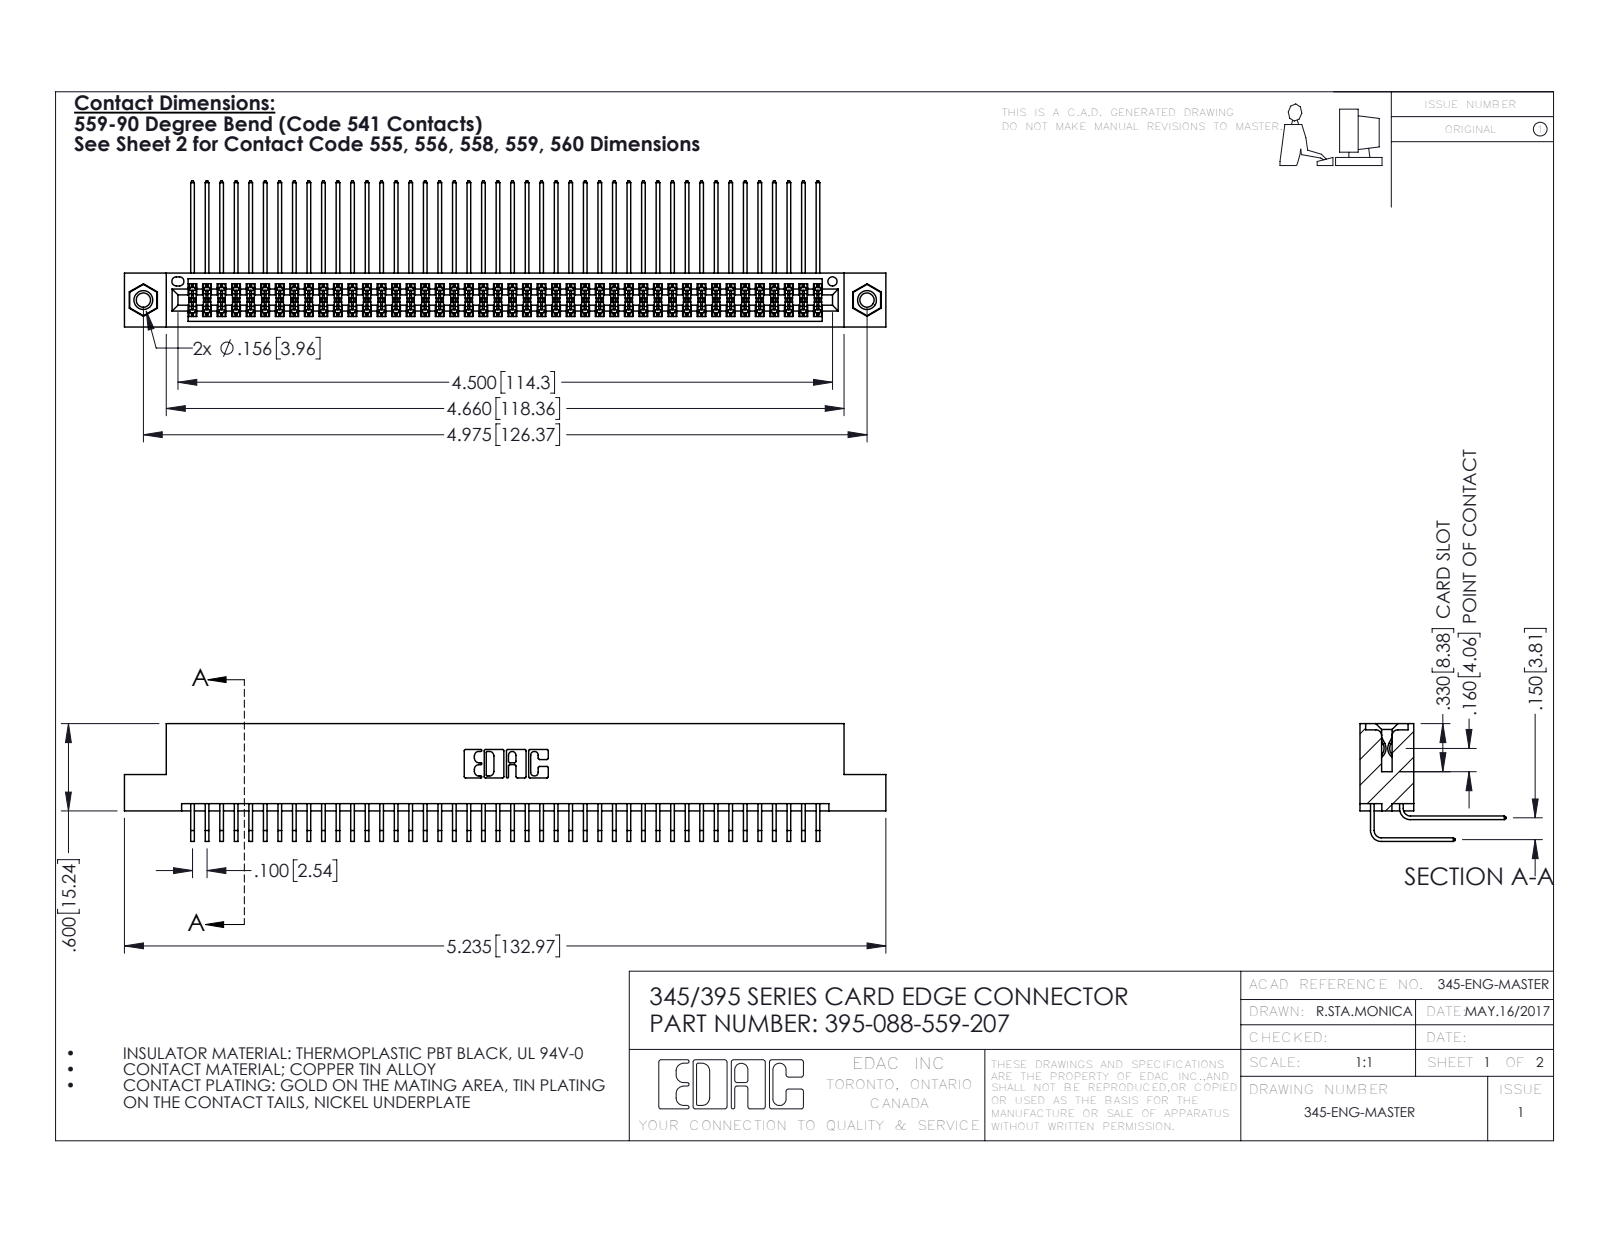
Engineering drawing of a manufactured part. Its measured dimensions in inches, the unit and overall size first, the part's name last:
Units: inches
Overall size (bounding box): 5.235 × 1.005 × 0.809
Round holes (diameter × count): ⌀0.098 ×2, ⌀0.125 ×2, ⌀0.156 ×2, ⌀0.064 ×1
Round bosses / shafts (diameter × count): ⌀0.155 ×2
Partial cylindrical surfaces — rounded edges, fillets, slot ends (radius × count): R0.006 ×133, R0.01 ×22, R0.007 ×6, R0.031 ×6, R0.026 ×3, R0.014 ×2, R0.019 ×2, R0.022 ×2
Main face-to-face distances: 0.072, 0.298, 0.2, 0.37, 0.098, 0.272, 0.025, 0.225, 0.175, 0.15
Hole centre spacings: 0.27, 4.739, 4.975
Volume: 0.82 in³ · Surface area: 34.57 in²
Bodies: 91 solids, 4762 faces (3192 planar, 1554 cylindrical, 16 other)
Part name (STEP PRODUCT): 345-292-001_558 559 Tail - 1; 345-250-001_345-250-005-103; 345 Part_Flush Mounting Lugs - 0.156 Dia-TI; 345-292-001_559 Tail - 2 (+1 more)
STEP written by: SolidWorks 2016 (CONFIG_CONTROL_DESIGN)
